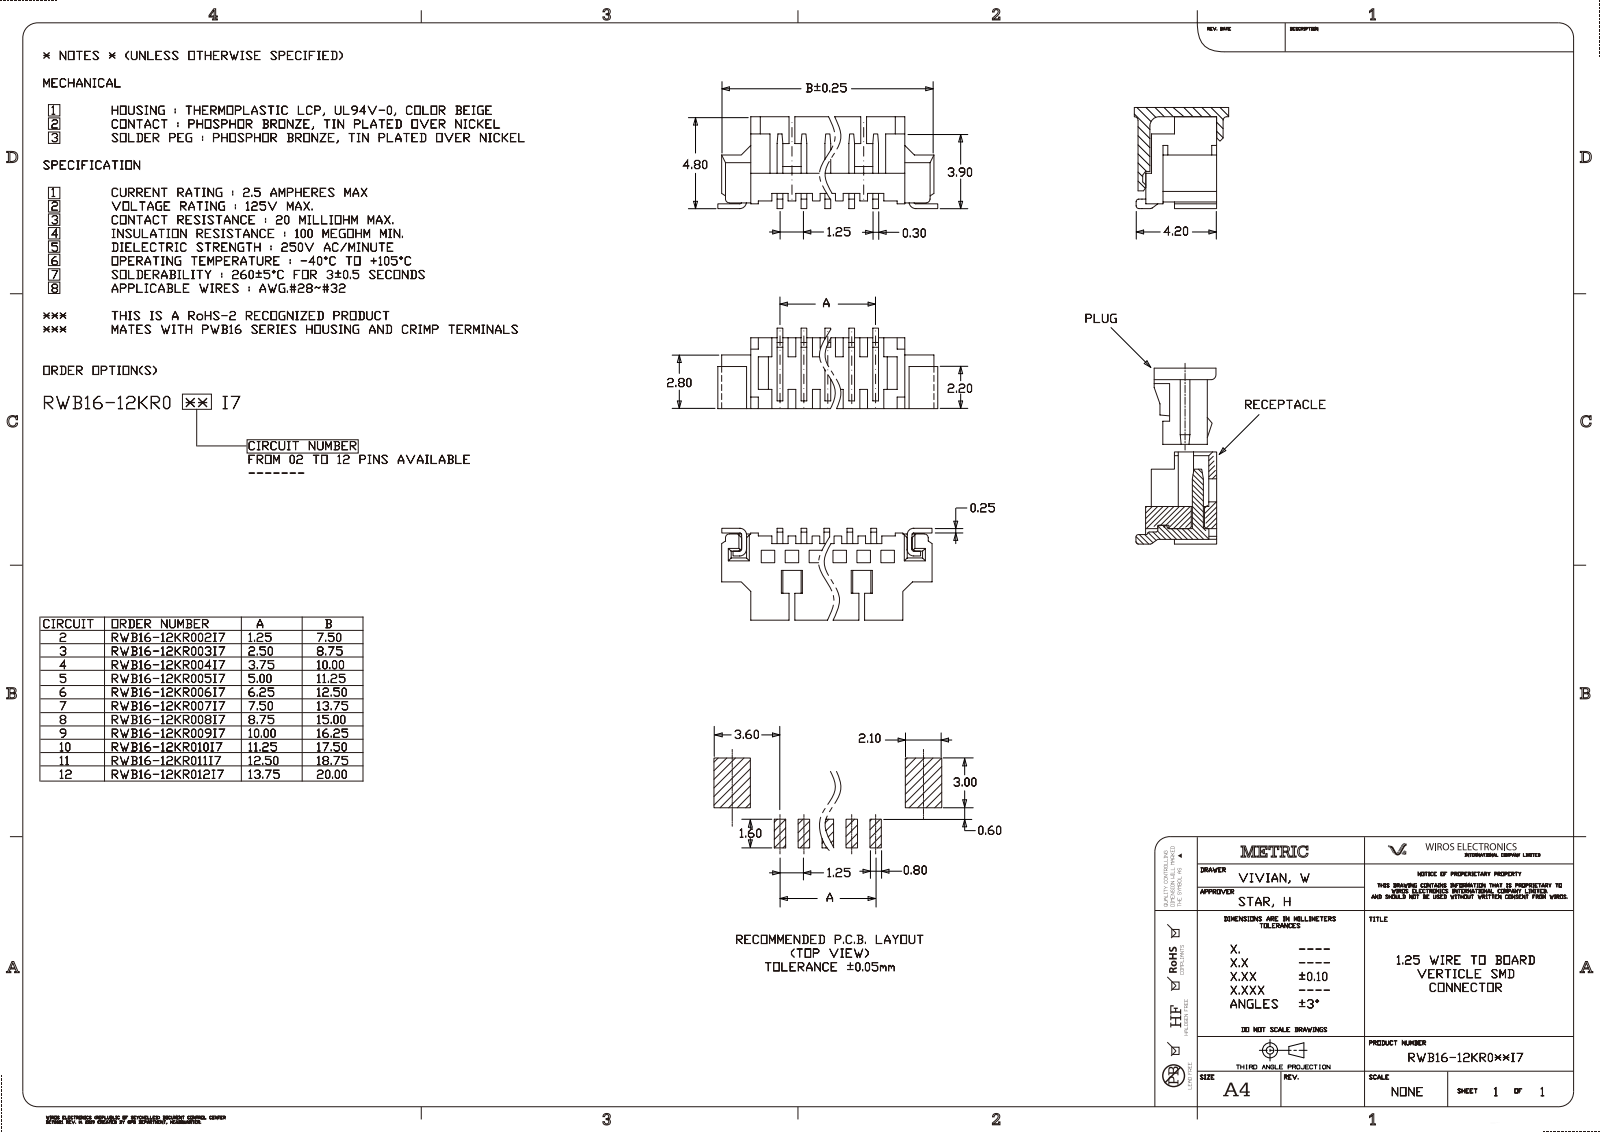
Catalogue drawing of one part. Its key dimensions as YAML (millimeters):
part_name: "AdmiAADF1a8h"
step_written_by: "UGS - NX 4.0 (AUTOMOTIVE_DESIGN)"
units: millimeters
bodies: {solids: 1, faces: 369, planar: 265, cylindrical: 104, other: 0}
overall_size: [10.45, 4.8, 4.48]
volume: 84
surface_area: 308
partial_cylinders:
  - {radius: 0.15, count: 16}
  - {radius: 0.2, count: 16}
  - {radius: 0.1, count: 4}
  - {radius: 0.35, count: 4}
face_to_face_distances: [1.25, 0.35, 2.8, 0.38, 3.7, 0.45, 1.85, 1.5, 3.5, 3.32]
